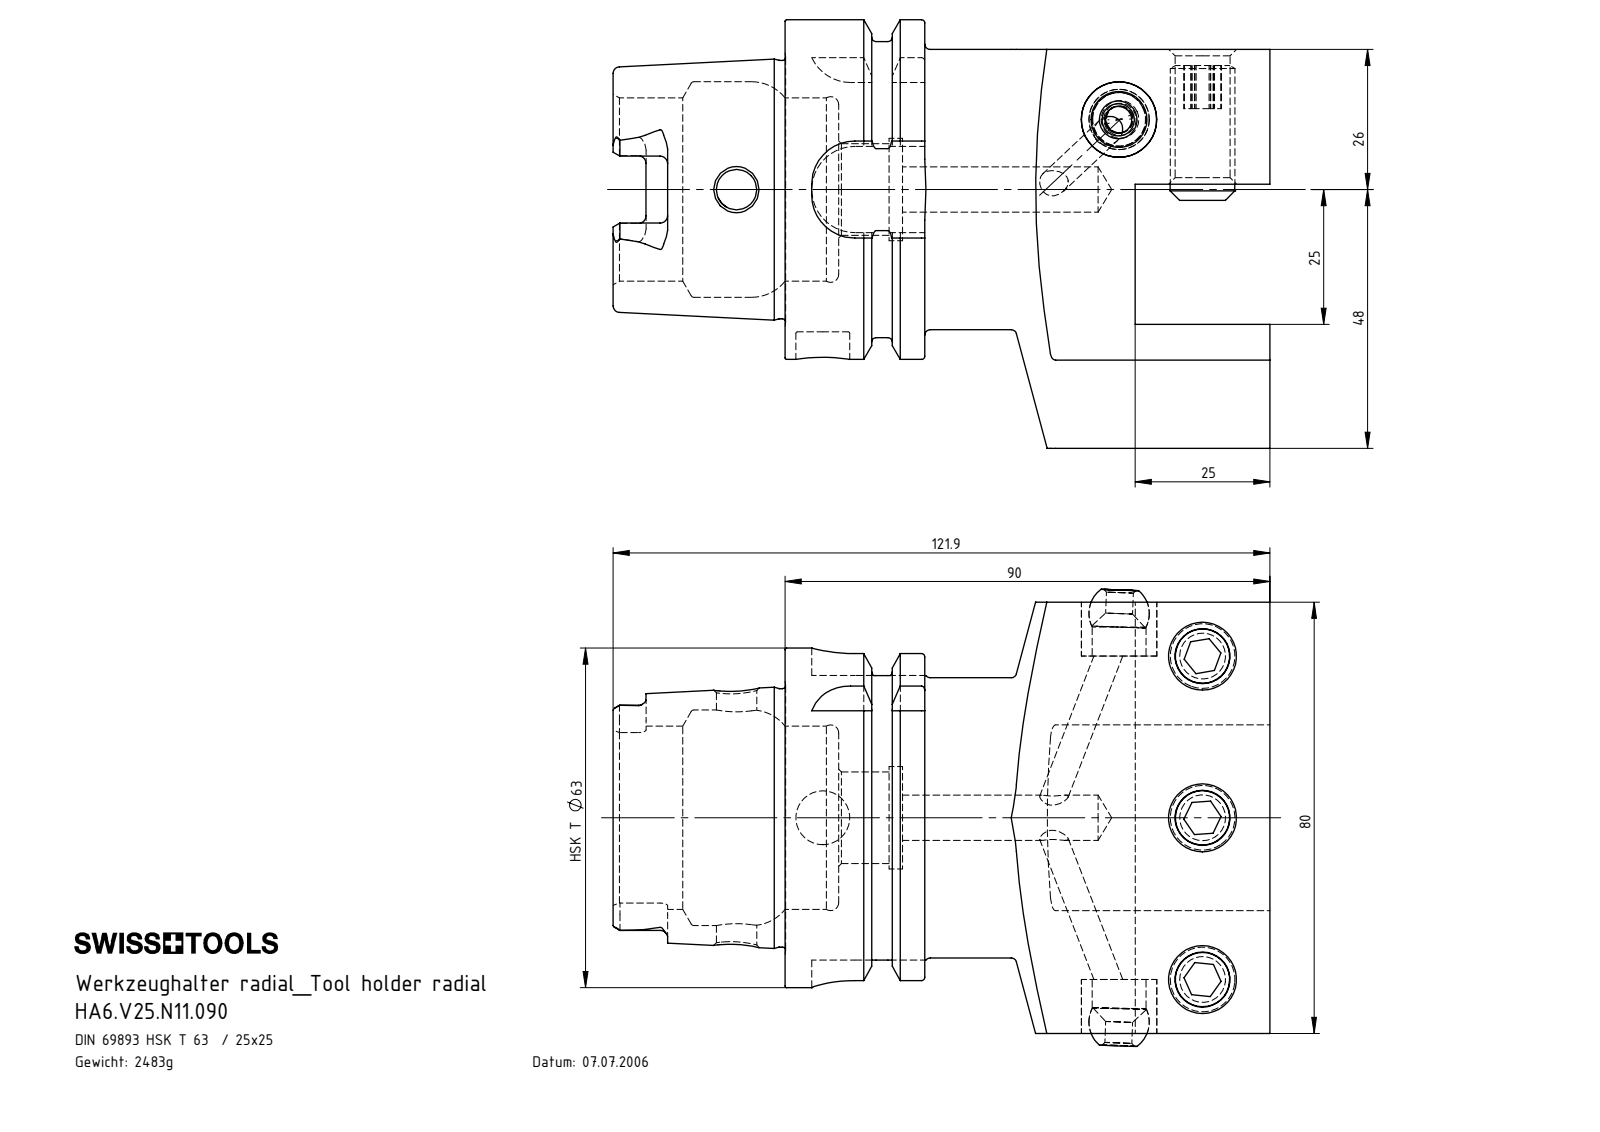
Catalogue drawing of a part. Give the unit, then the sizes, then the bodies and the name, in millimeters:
Units: millimetres
Overall size (bounding box): 121.9 × 85.63 × 79.5
Round holes (diameter × count): ⌀5 ×4, ⌀10.2 ×3, ⌀10 ×2, ⌀7.5 ×1, ⌀8.4 ×1, ⌀14 ×1, ⌀17 ×1, ⌀19 ×1, ⌀34 ×1, ⌀40 ×1
Round bosses / shafts (diameter × count): ⌀12 ×3, ⌀63 ×1, ⌀54.95 ×1, ⌀52 ×1, ⌀47.94 ×1
Partial cylindrical surfaces — rounded edges, fillets, slot ends (radius × count): R1.4 ×6, R2.88 ×4, R8 ×4, R51 ×1
Main face-to-face distances: 25, 51, 80, 26, 23, 49, 74, 65, 90, 13.6
Hole centre spacings: 30, 76.62, 60, 70.5, 72.18
Volume: 317 475 mm³ · Surface area: 57 873 mm²
Bodies: 8 solids, 271 faces (86 planar, 79 cylindrical, 106 other)
Part name (STEP PRODUCT): KU1-U14.001.012; ISO 4026 - M12 x 25; HA6-V25.N11.090_B; KU1-U14.001.012_2 (+2 more)
STEP written by: SolidWorks 2017 (AUTOMOTIVE_DESIGN)
